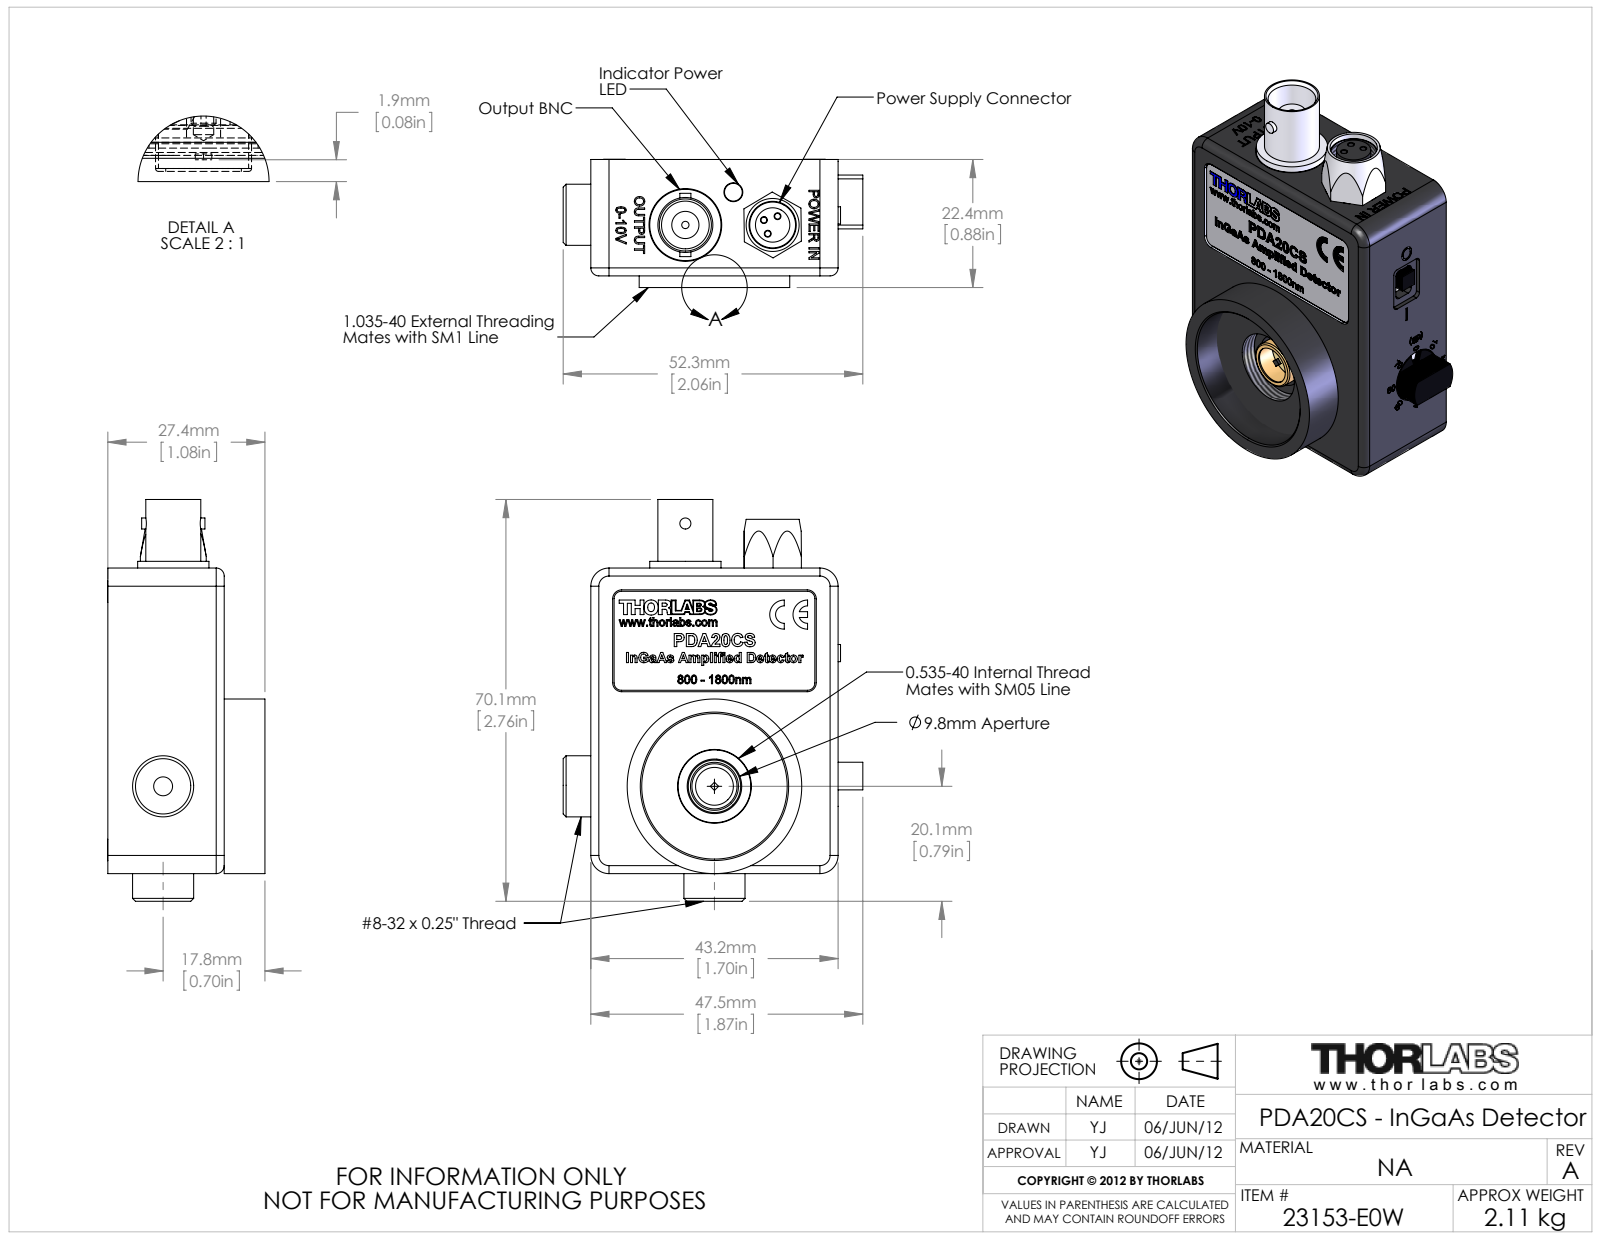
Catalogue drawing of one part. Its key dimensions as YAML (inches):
part_name: "13053-001_Etching; 23155-002_PDA20CS-LB1; FGA21; SH2S019-1_HX-SHCS 0.086-56x0.188x0.188-N (+8 more)"
step_written_by: "SolidWorks 2011 (AUTOMOTIVE_DESIGN)"
units: inches
bodies: {solids: 24, faces: 2310, planar: 1156, cylindrical: 351, other: 803}
overall_size: [2.761, 2.06, 1.082]
volume: 1.566
surface_area: 48.88
round_holes:
  - {diameter: 0.037, count: 9}
  - {diameter: 0.032, count: 8}
  - {diameter: 0.07, count: 7}
  - {diameter: 0.096, count: 7}
  - {diameter: 0.033, count: 6}
  - {diameter: 0.125, count: 4}
  - {diameter: 0.2, count: 4}
  - {diameter: 0.028, count: 3}
  - {diameter: 0.03, count: 3}
  - {diameter: 0.039, count: 3}
  - {diameter: 0.05, count: 3}
  - {diameter: 0.13, count: 2}
round_bosses_or_shafts:
  - {diameter: 0.086, count: 7}
  - {diameter: 0.02, count: 6}
  - {diameter: 0.147, count: 4}
  - {diameter: 0.14, count: 3}
  - {diameter: 0.018, count: 3}
  - {diameter: 0.42, count: 2}
  - {diameter: 0.37, count: 2}
  - {diameter: 0.236, count: 2}
partial_cylinders:
  - {radius: 0.125, count: 23}
  - {radius: 0.031, count: 14}
  - {radius: 0.095, count: 8}
  - {radius: 0.05, count: 4}
  - {radius: 0.055, count: 4}
  - {radius: 0.024, count: 3}
  - {radius: 0.062, count: 3}
  - {radius: 0.222, count: 3}
face_to_face_distances: [0.063, 0.502, 0.565, 0.1, 0.063, 0.502, 0.439, 0.07, 0.05, 0.55]
hole_center_spacings: [0.1, 0.141, 0.079, 0.126, 0.128, 0.2, 0.203, 0.28]
